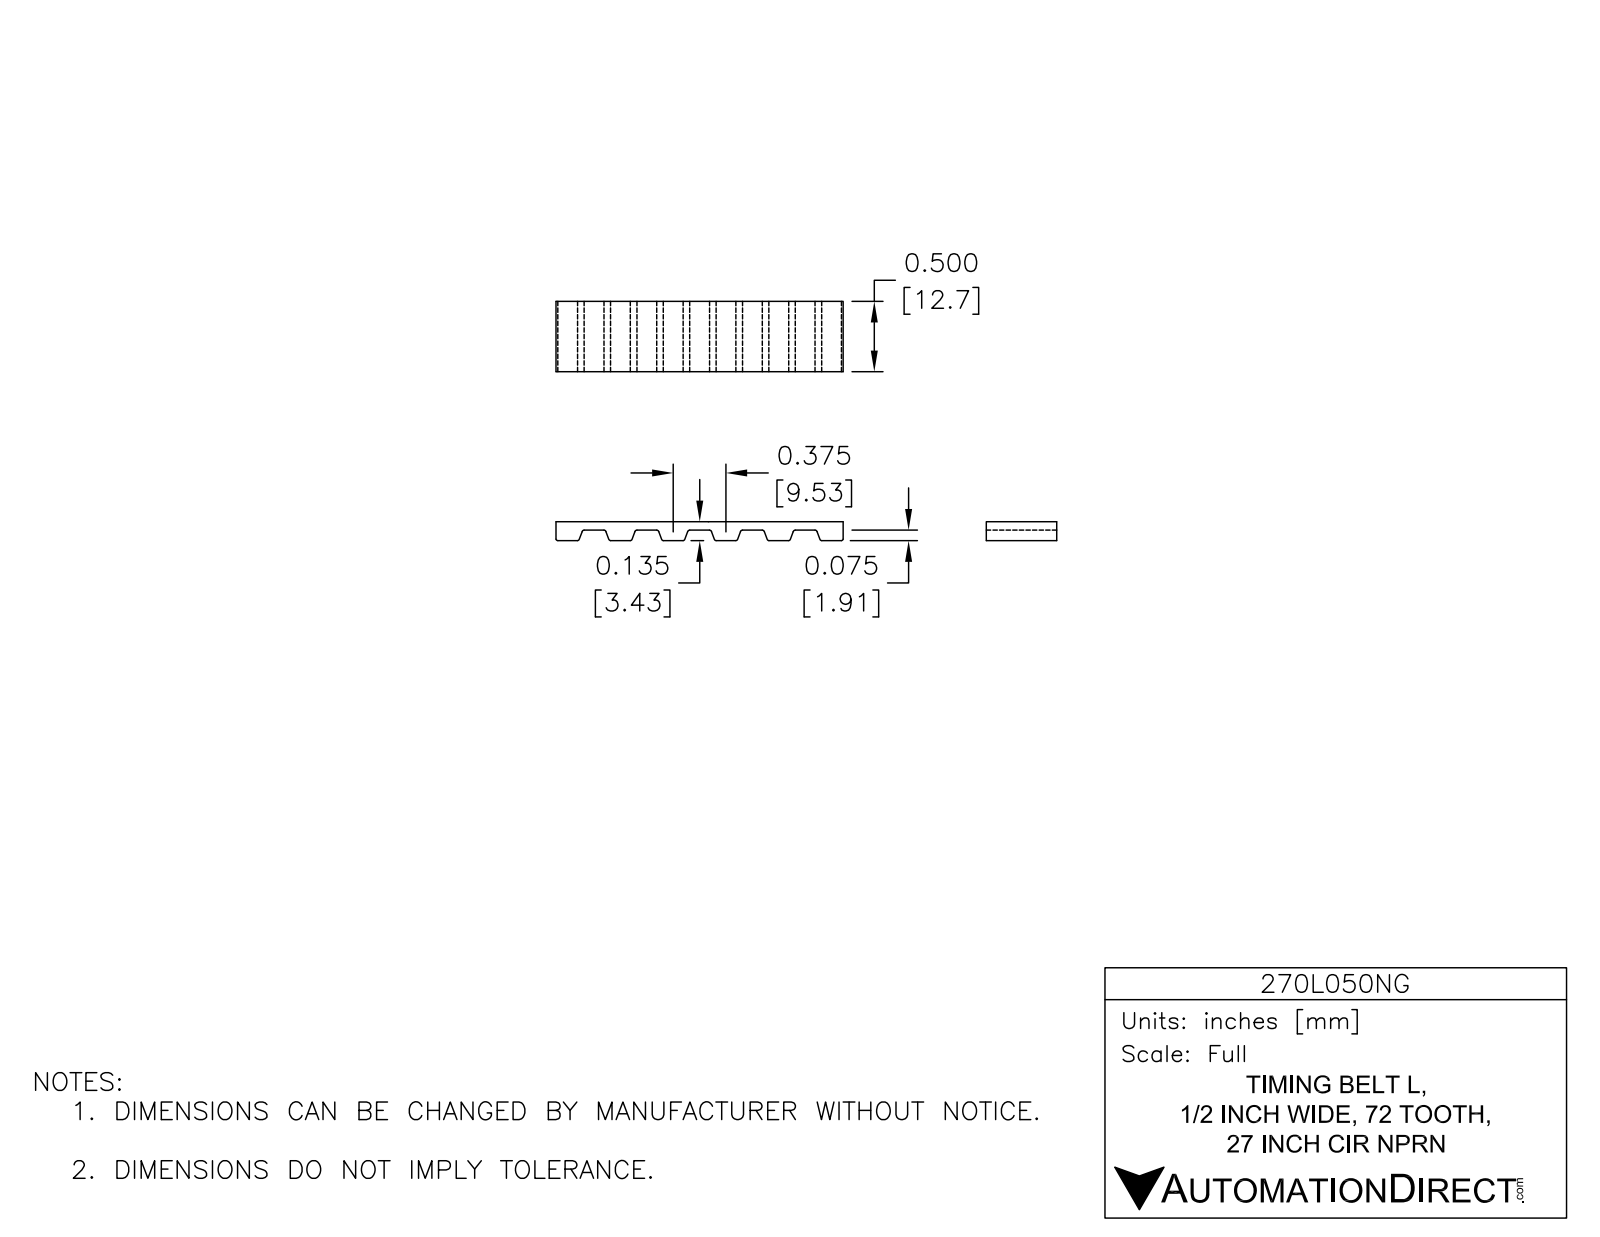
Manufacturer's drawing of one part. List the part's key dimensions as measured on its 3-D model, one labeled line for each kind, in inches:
Part name (STEP PRODUCT): 270L050NG
STEP written by: SolidWorks 2014 (AUTOMOTIVE_DESIGN)
Units: inches
Bodies: 1 solid, 591 faces (265 planar, 326 cylindrical, 0 other)
Overall size (bounding box): 11.788 × 3 × 0.5
Volume: 1.219 in³ · Surface area: 34.88 in²
Partial cylindrical surfaces — rounded edges, fillets, slot ends (radius × count): R0.02 ×284, R1.435 ×2, R1.5 ×2
Main face-to-face distances: 0.065, 2.935, 3, 0.5, 2.87, 0.14, 2.86, 0.075, 2.795, 2.72
